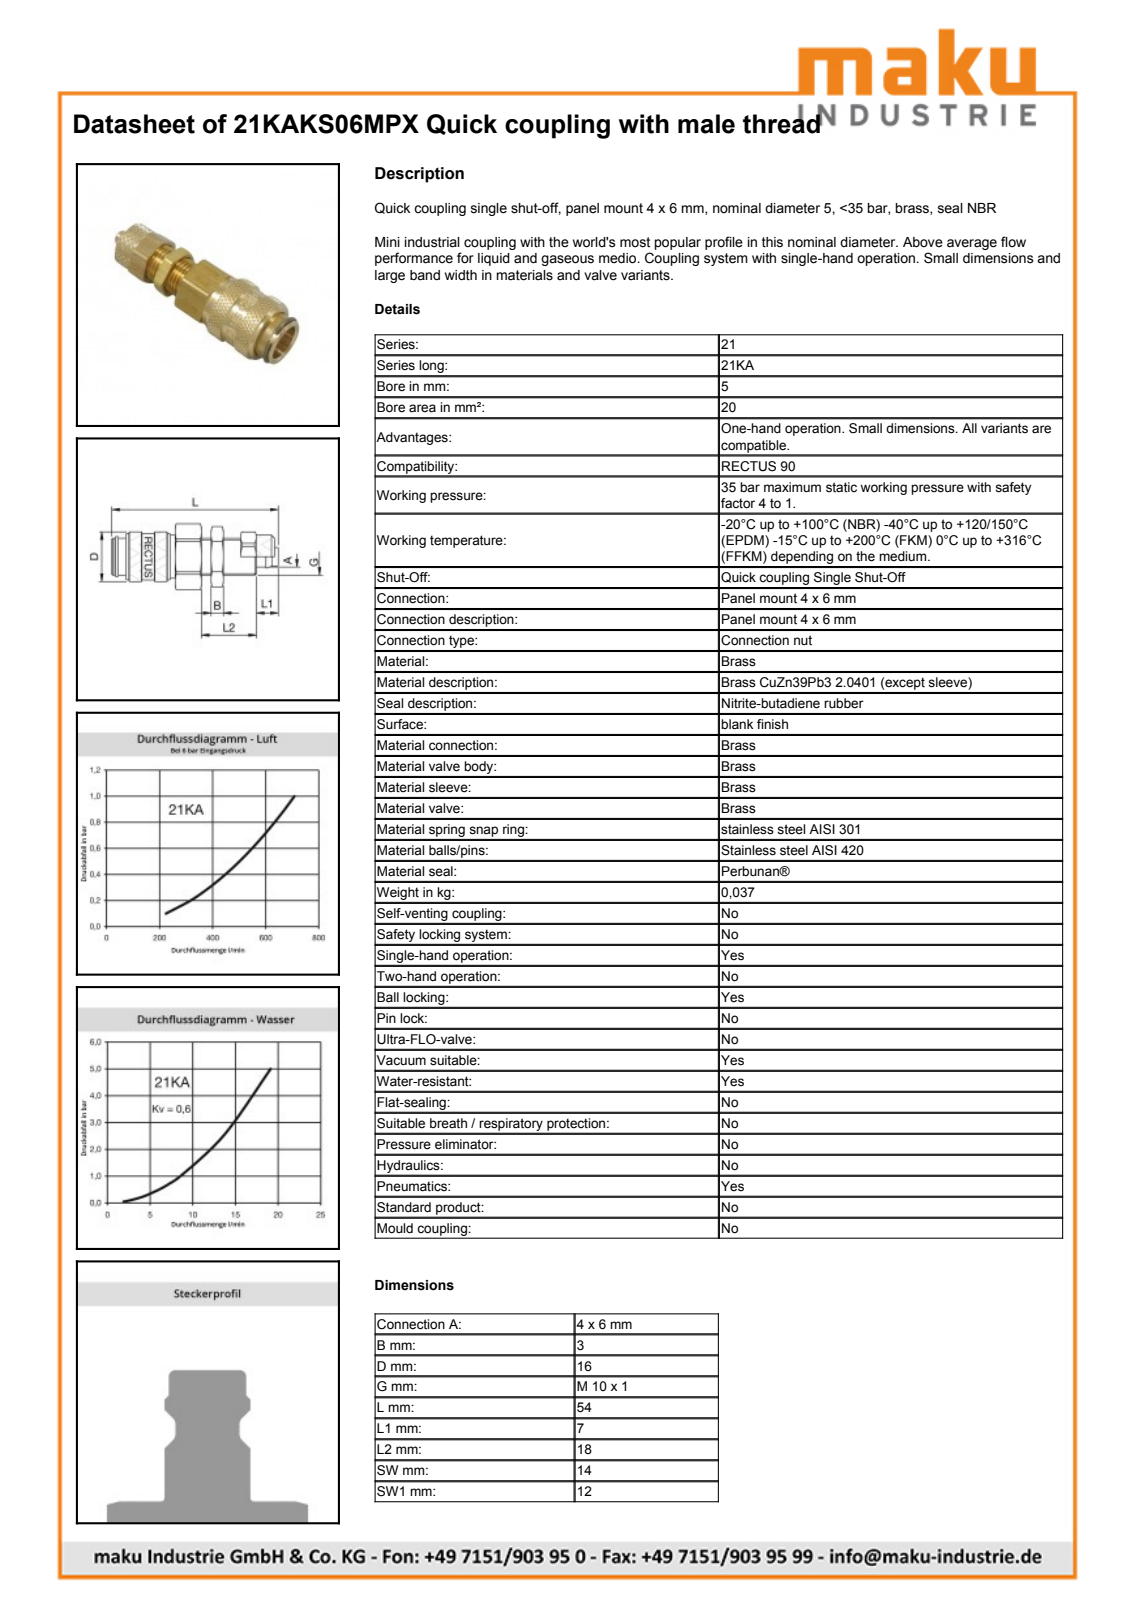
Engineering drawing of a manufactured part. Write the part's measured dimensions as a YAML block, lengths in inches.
part_name: "D107913"
step_written_by: "Autodesk Inventor 2013 (AUTOMOTIVE_DESIGN)"
units: inches
bodies: {solids: 2, faces: 525, planar: 167, cylindrical: 80, other: 278}
overall_size: [2.132, 0.636, 0.636]
volume: 0.415
surface_area: 7.173
round_holes:
  - {diameter: 0.244, count: 1}
  - {diameter: 0.413, count: 1}
  - {diameter: 0.478, count: 1}
  - {diameter: 0.551, count: 1}
round_bosses_or_shafts:
  - {diameter: 0.636, count: 1}
  - {diameter: 0.594, count: 1}
  - {diameter: 0.472, count: 1}
  - {diameter: 0.449, count: 1}
  - {diameter: 0.439, count: 1}
  - {diameter: 0.428, count: 1}
  - {diameter: 0.394, count: 1}
  - {diameter: 0.181, count: 1}
partial_cylinders:
  - {radius: 0.264, count: 1}
  - {radius: 0.266, count: 1}
  - {radius: 0.293, count: 1}
  - {radius: 0.311, count: 1}
face_to_face_distances: [0.551, 0.472, 1.148, 1.852, 0.705, 0.236, 2.089, 0.941, 0.197, 1.02]
